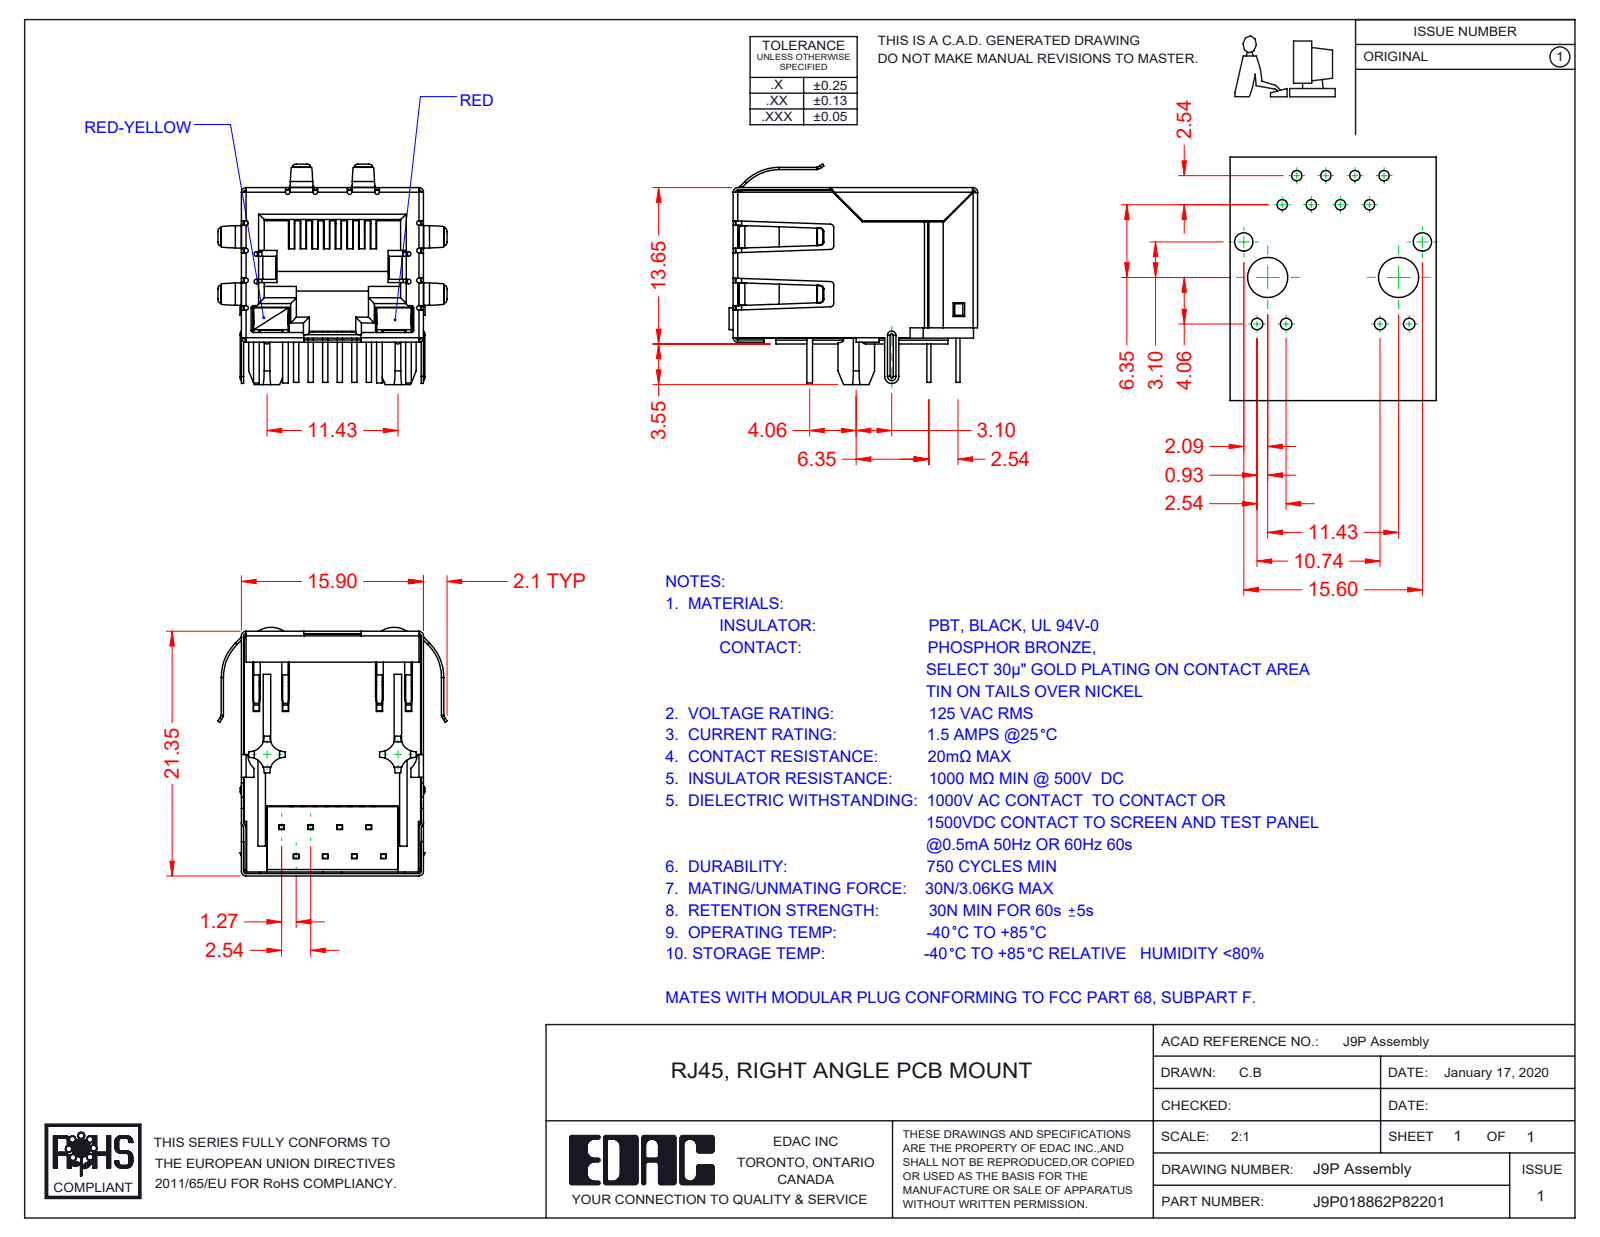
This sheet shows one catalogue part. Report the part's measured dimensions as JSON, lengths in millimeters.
{"part_name": "9P-LED Shield; 9P-LED Insulator; J9P018862P82202; 9P-LED Contacts (+4 more)", "step_written_by": "SolidWorks 2016 (CONFIG_CONTROL_DESIGN)", "units": "millimeters", "bodies": {"solids": 13, "faces": 1474, "planar": 1042, "cylindrical": 338, "other": 94}, "overall_size": [21.7, 20, 19.25], "volume_mm3": 2687, "surface_area_mm2": 7515, "partial_cylinders_radius": [[0.2, 39], [0.5, 22], [0.3, 20], [0.4, 16], [1.3, 8], [0.23, 5], [0.11, 4], [0.31, 4]], "face_to_face_distances": [15.45, 15.7, 15.65, 0.35, 0.54, 15.5, 12.36, 0.6, 1.4, 0.59]}
